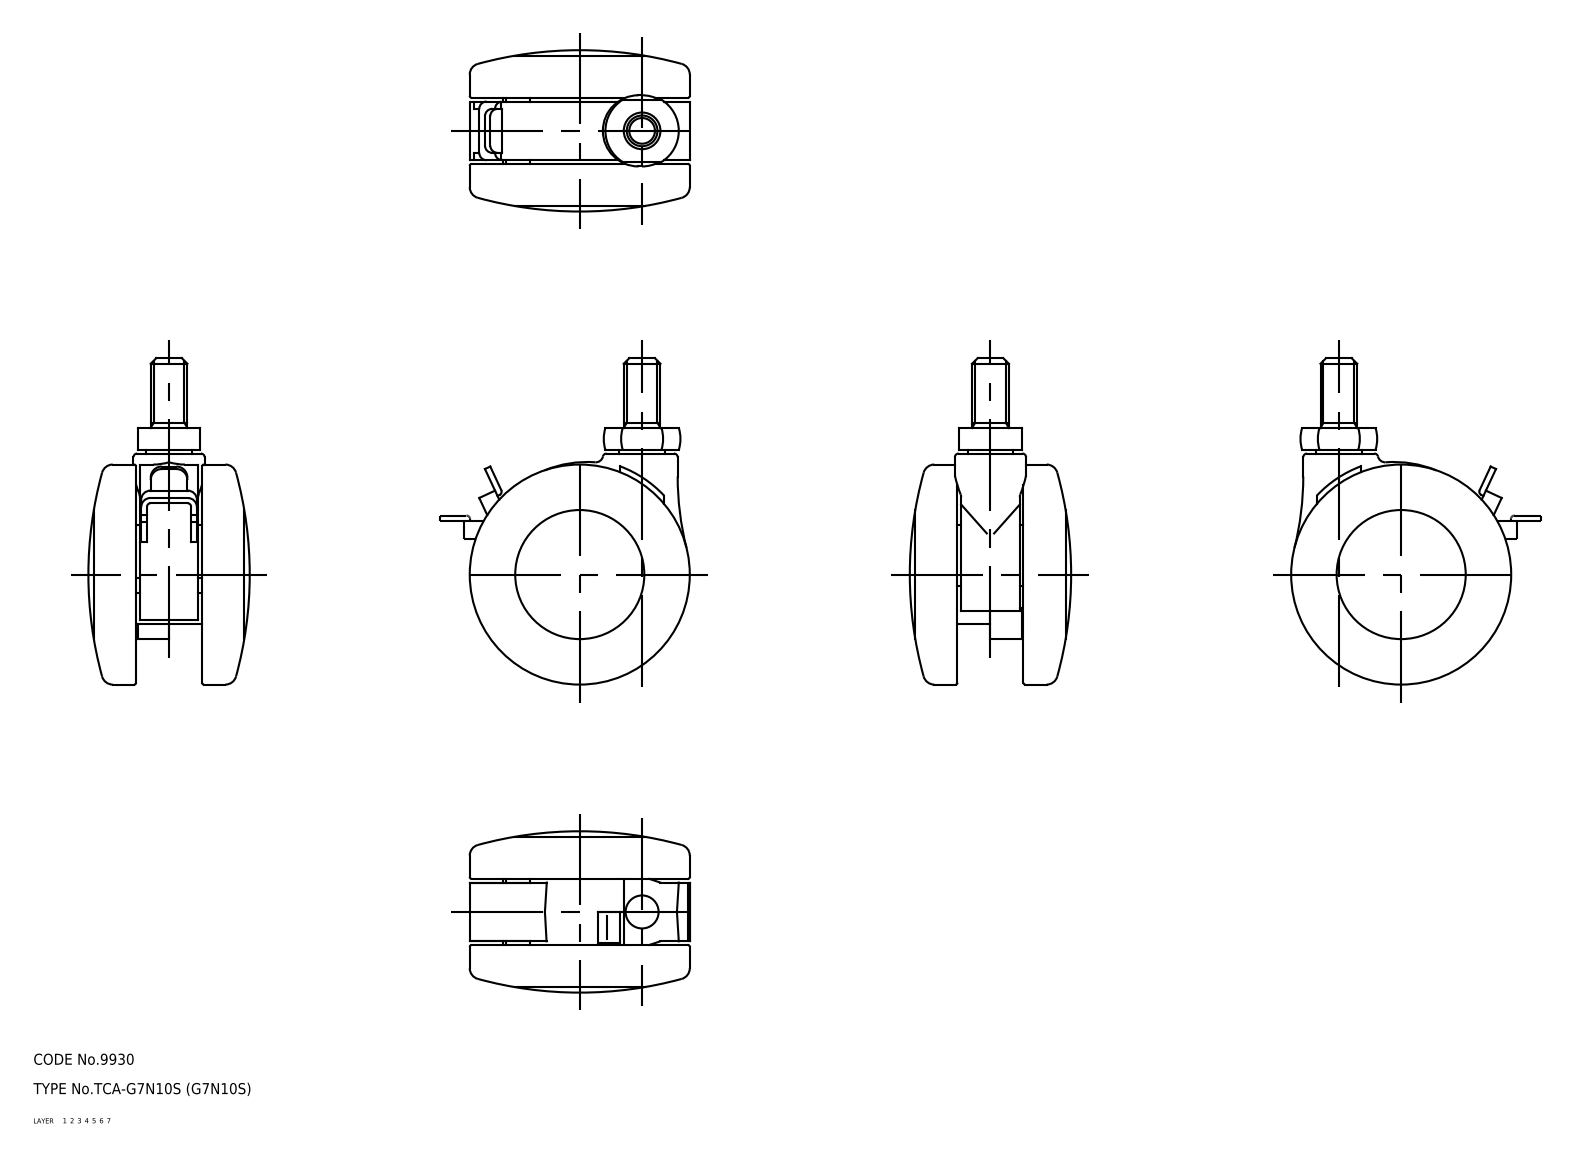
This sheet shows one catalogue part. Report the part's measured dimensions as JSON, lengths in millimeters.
{"part_name": "wheel; main shaft; lever; G7N10S_12982_36", "step_written_by": "CADfix (AUTOMOTIVE_DESIGN)", "units": "millimeters", "bodies": {"solids": 5, "faces": 194, "planar": 0, "cylindrical": 0, "other": 194}, "overall_size": [89, 68, 44], "volume_mm3": 92939, "surface_area_mm2": 34221}
